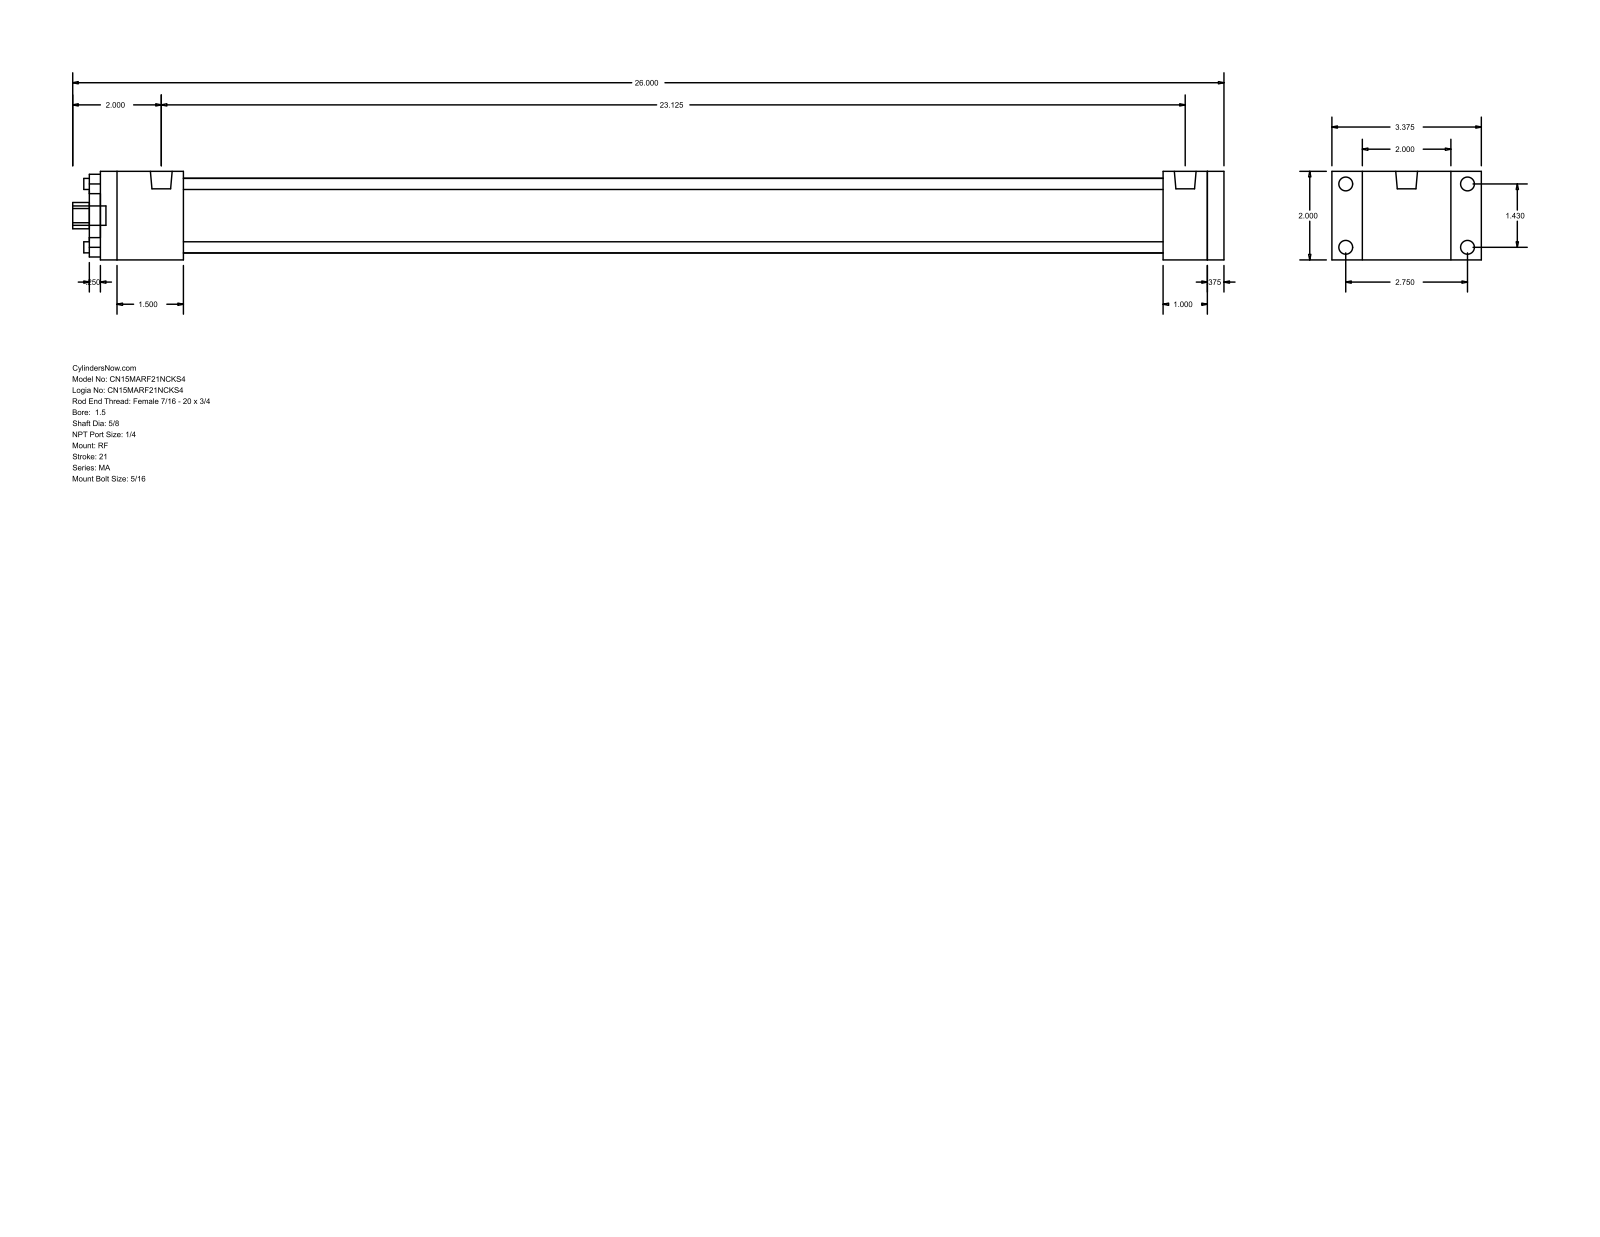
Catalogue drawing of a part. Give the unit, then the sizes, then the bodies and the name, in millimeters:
Units: millimetres
Overall size (bounding box): 660.4 × 85.72 × 50.8
Round holes (diameter × count): ⌀6.35 ×4, ⌀15.88 ×1, ⌀28.57 ×1, ⌀42.93 ×1
Round bosses / shafts (diameter × count): ⌀7.94 ×8, ⌀12.49 ×2, ⌀11.11 ×1
Partial cylindrical surfaces — rounded edges, fillets, slot ends (radius × count): R7.54 ×1
Main face-to-face distances: 50.8, 9.52, 635, 644.52, 609.6, 25.4, 34.92, 47.62, 561.98, 587.38
Hole centre spacings: 25.68, 36.32, 51.36
Bodies: 0 solids, 92 faces (64 planar, 28 cylindrical, 0 other)
Part name (STEP PRODUCT): MA_RF__0150_0.625
STEP written by: GSSL Pune (CONFIG_CONTROL_DESIGN)
